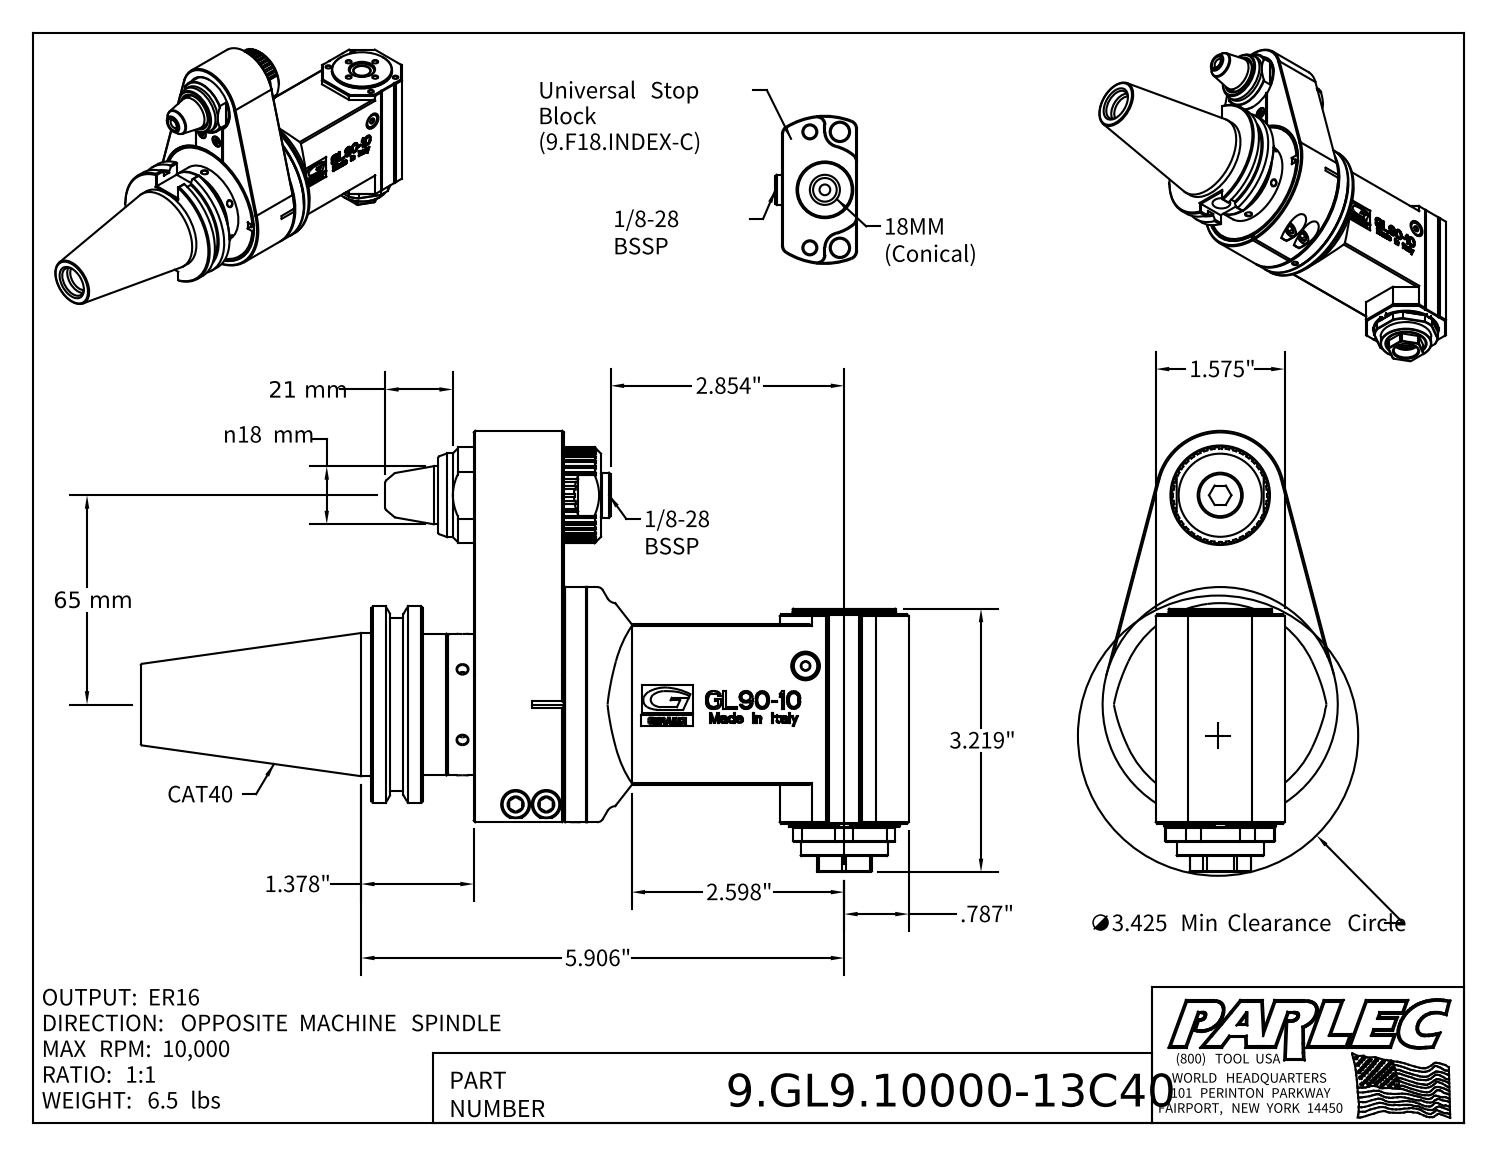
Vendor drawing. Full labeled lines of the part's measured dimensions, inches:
Part name (STEP PRODUCT): 9.GL9.10000-13C40; 9_GL9_10000
STEP written by: Autodesk Inventor 2022 (AUTOMOTIVE_DESIGN)
Units: inches
Bodies: 79 solids, 2732 faces (1850 planar, 361 cylindrical, 521 other)
Overall size (bounding box): 9.386 × 5.394 × 2.874
Volume: 41.59 in³ · Surface area: 310.2 in²
Round holes (diameter × count): ⌀0.13 ×11, ⌀0.098 ×7, ⌀0.157 ×7, ⌀0.236 ×5, ⌀0.106 ×4, ⌀0.118 ×4, ⌀0.197 ×4, ⌀0.354 ×3, ⌀0.165 ×2, ⌀0.173 ×2, ⌀0.335 ×2, ⌀0.512 ×2
Round bosses / shafts (diameter × count): ⌀0.157 ×4, ⌀0.197 ×3, ⌀0.118 ×3, ⌀1.378 ×2, ⌀1.26 ×2, ⌀1.142 ×2, ⌀0.866 ×2, ⌀0.335 ×2
Partial cylindrical surfaces — rounded edges, fillets, slot ends (radius × count): R0.008 ×8, R0.079 ×5, R0.089 ×4, R0.074 ×2, R0.085 ×2, R0.097 ×2, R0.133 ×2, R0.158 ×2
Main face-to-face distances: 1.102, 0.118, 0.276, 0.157, 0.512, 0.827, 0.354, 0.236, 0.591, 1.575
Hole centre spacings: 1.201, 0.728, 2.08, 0.394, 0.435, 0.557, 0.631, 0.986
